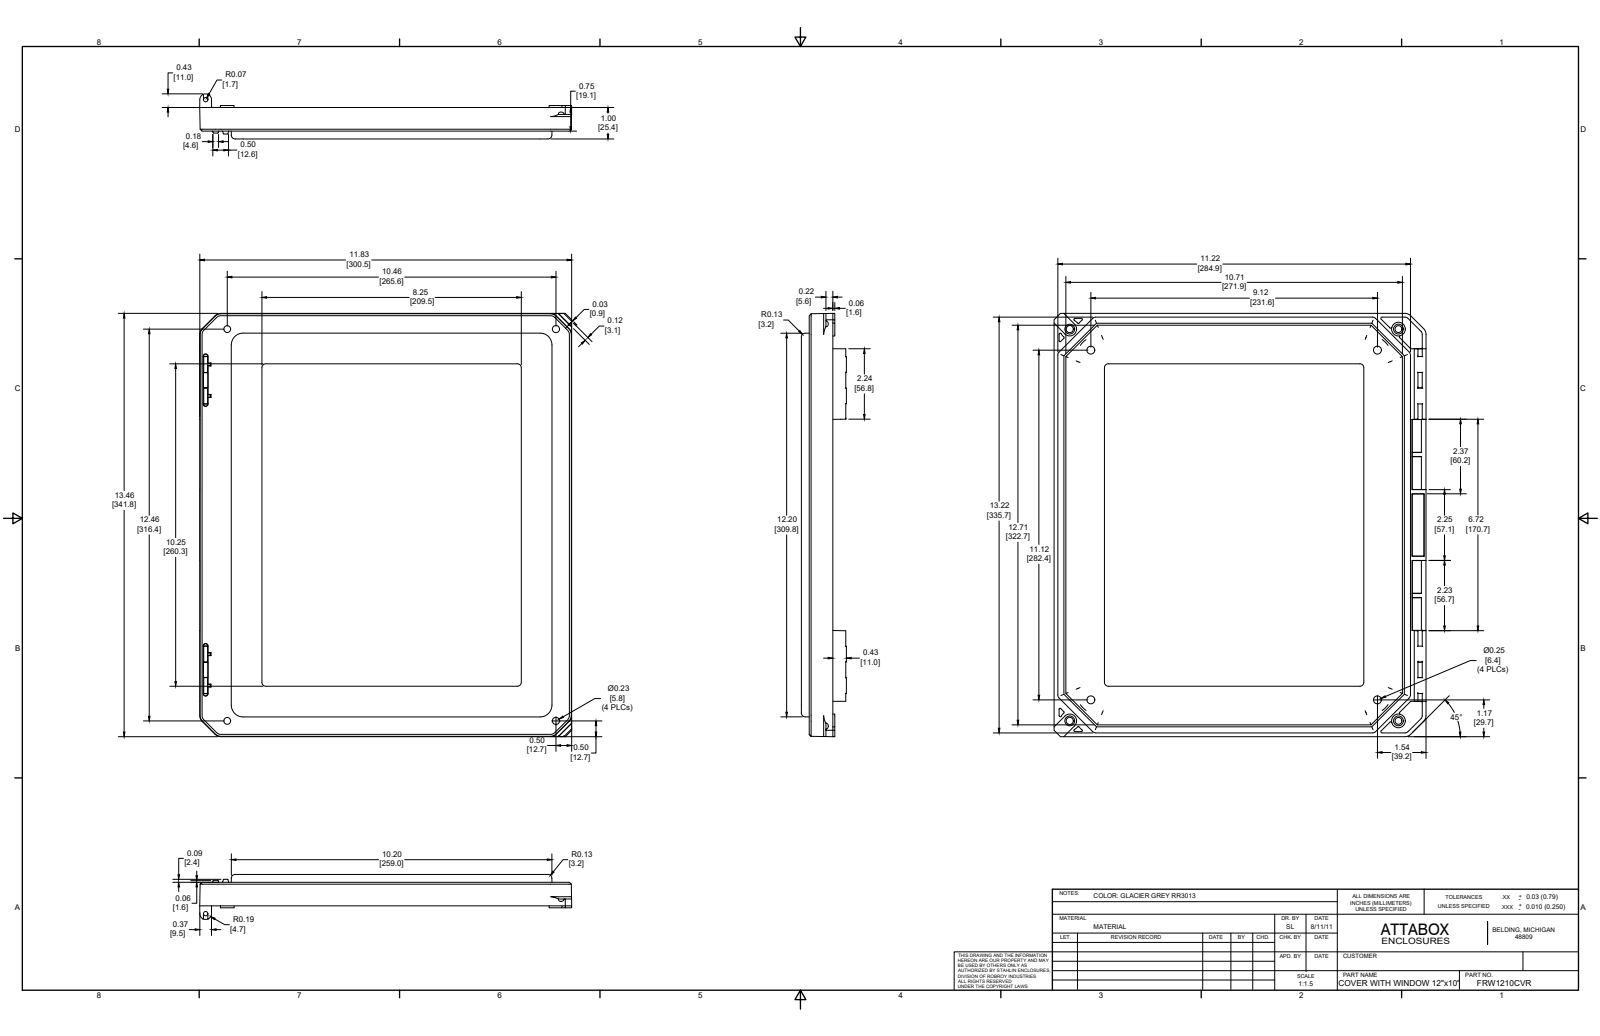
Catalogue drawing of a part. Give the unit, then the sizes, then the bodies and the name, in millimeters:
Units: millimetres
Overall size (bounding box): 341.8 × 300.5 × 36.4
Round holes (diameter × count): ⌀6.4 ×4, ⌀5.6 ×2, ⌀5.8 ×2, ⌀8 ×2, ⌀3.5 ×1
Round bosses / shafts (diameter × count): ⌀11 ×1, ⌀11 ×1
Partial cylindrical surfaces — rounded edges, fillets, slot ends (radius × count): R0.8 ×27, R2.4 ×16, R3.2 ×16, R1.6 ×15, R0.3 ×14, R1.5 ×11, R1 ×10, R1.6 ×9
Main face-to-face distances: 3.2, 6.4, 3.2, 9.5, 19.1, 25.4, 22.2, 15.9, 9.5, 3.4
Hole centre spacings: 299.9, 24, 24.1, 231.6, 249.1, 249.2, 265.6, 282.4
Volume: 404 300 mm³ · Surface area: 169 200 mm²
Bodies: 1 solid, 576 faces (230 planar, 198 cylindrical, 148 other)
Part name (STEP PRODUCT): FRW1210CVR
STEP written by: SolidWorks 2019 (AUTOMOTIVE_DESIGN)
